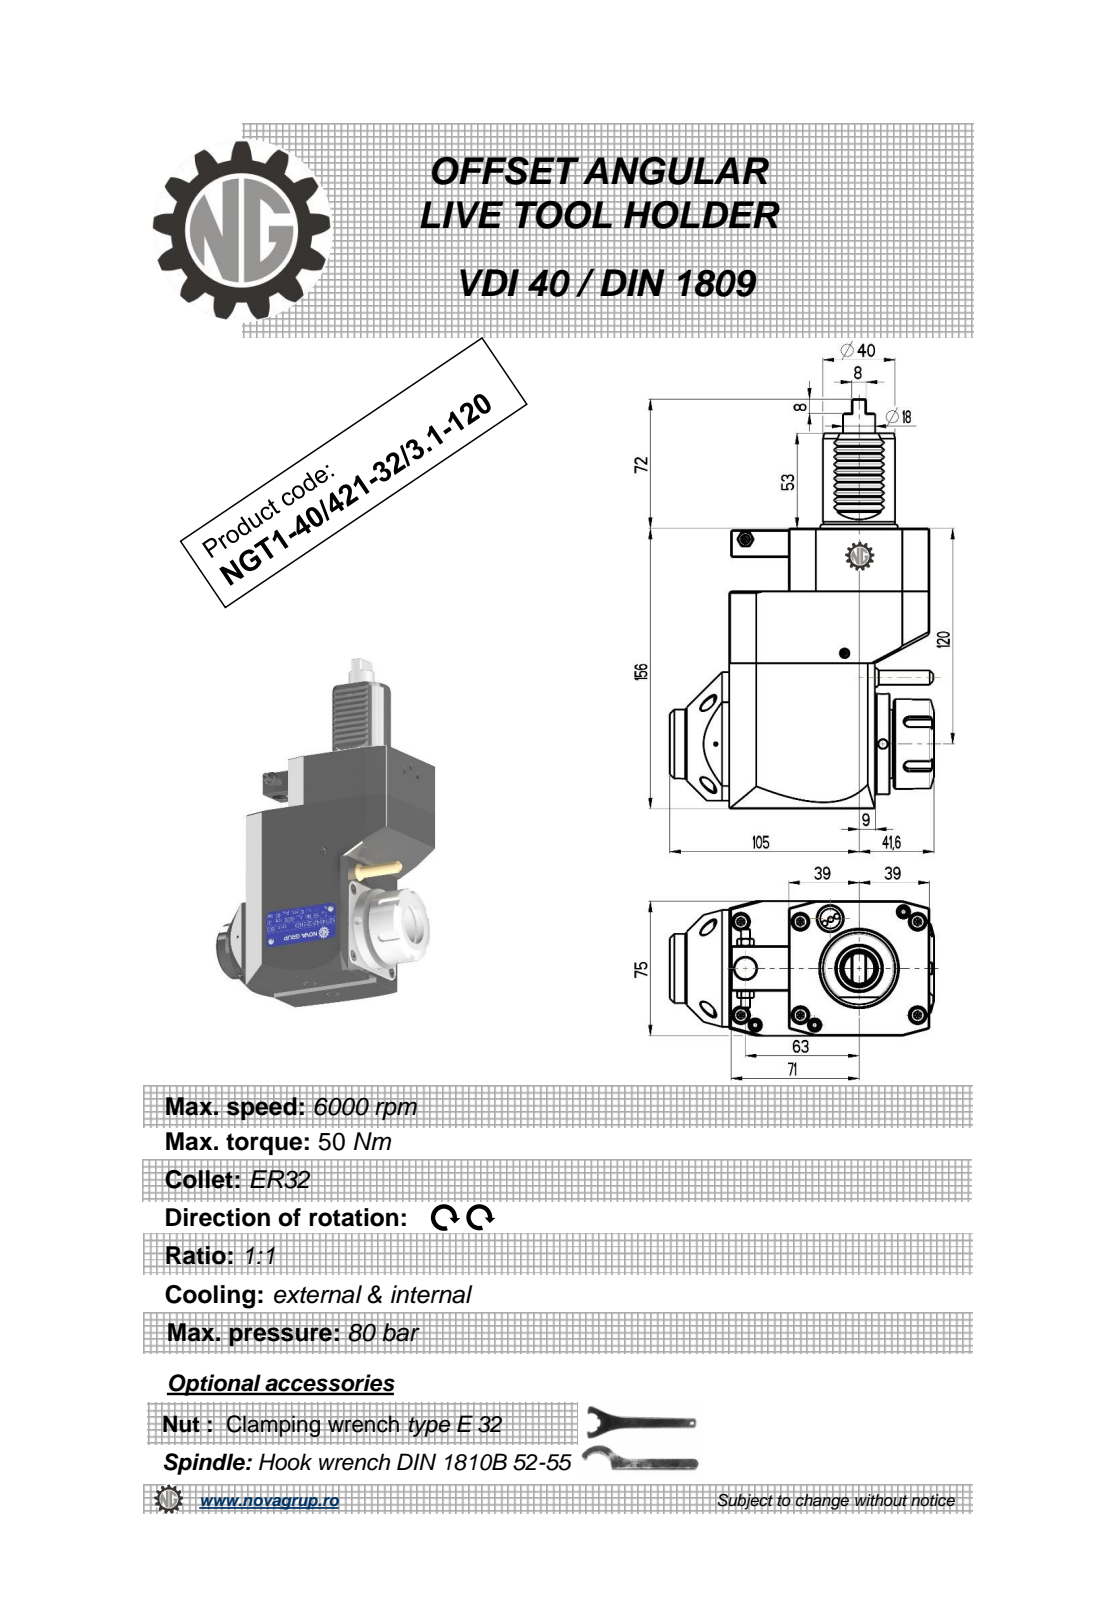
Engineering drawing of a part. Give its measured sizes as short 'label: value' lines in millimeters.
name: NGT1_40_421_32_3_1_120
written by: PRO/ENGINEER BY PARAMETRIC TECHNOLOGY CORPORATION, 2010280 (CONFIG_CONTROL_DESIGN)
unit: mm
bodies: 1 solid, 429 faces (207 planar, 87 cylindrical, 135 other)
size: 228 × 146.6 × 75
volume: 1 214 000 mm³; area: 89 883 mm²
holes: 3× ⌀5, 1× ⌀3, 1× ⌀4.2, 1× ⌀9.5, 1× ⌀12, 1× ⌀27
bosses: 1× ⌀56, 1× ⌀50, 1× ⌀43, 1× ⌀40, 1× ⌀38.5, 1× ⌀17.8, 1× ⌀11.2, 1× ⌀8.96
rounds: 12× R0.26, 10× R0.3, 6× R0.22, 5× R3, 2× R0.8, 1× R0.5, 1× R40
face distances: 75, 156, 111, 33, 35, 121, 81, 30, 48, 78
hole spacings: 40.93, 76.25, 77.5, 112.5, 137.15
